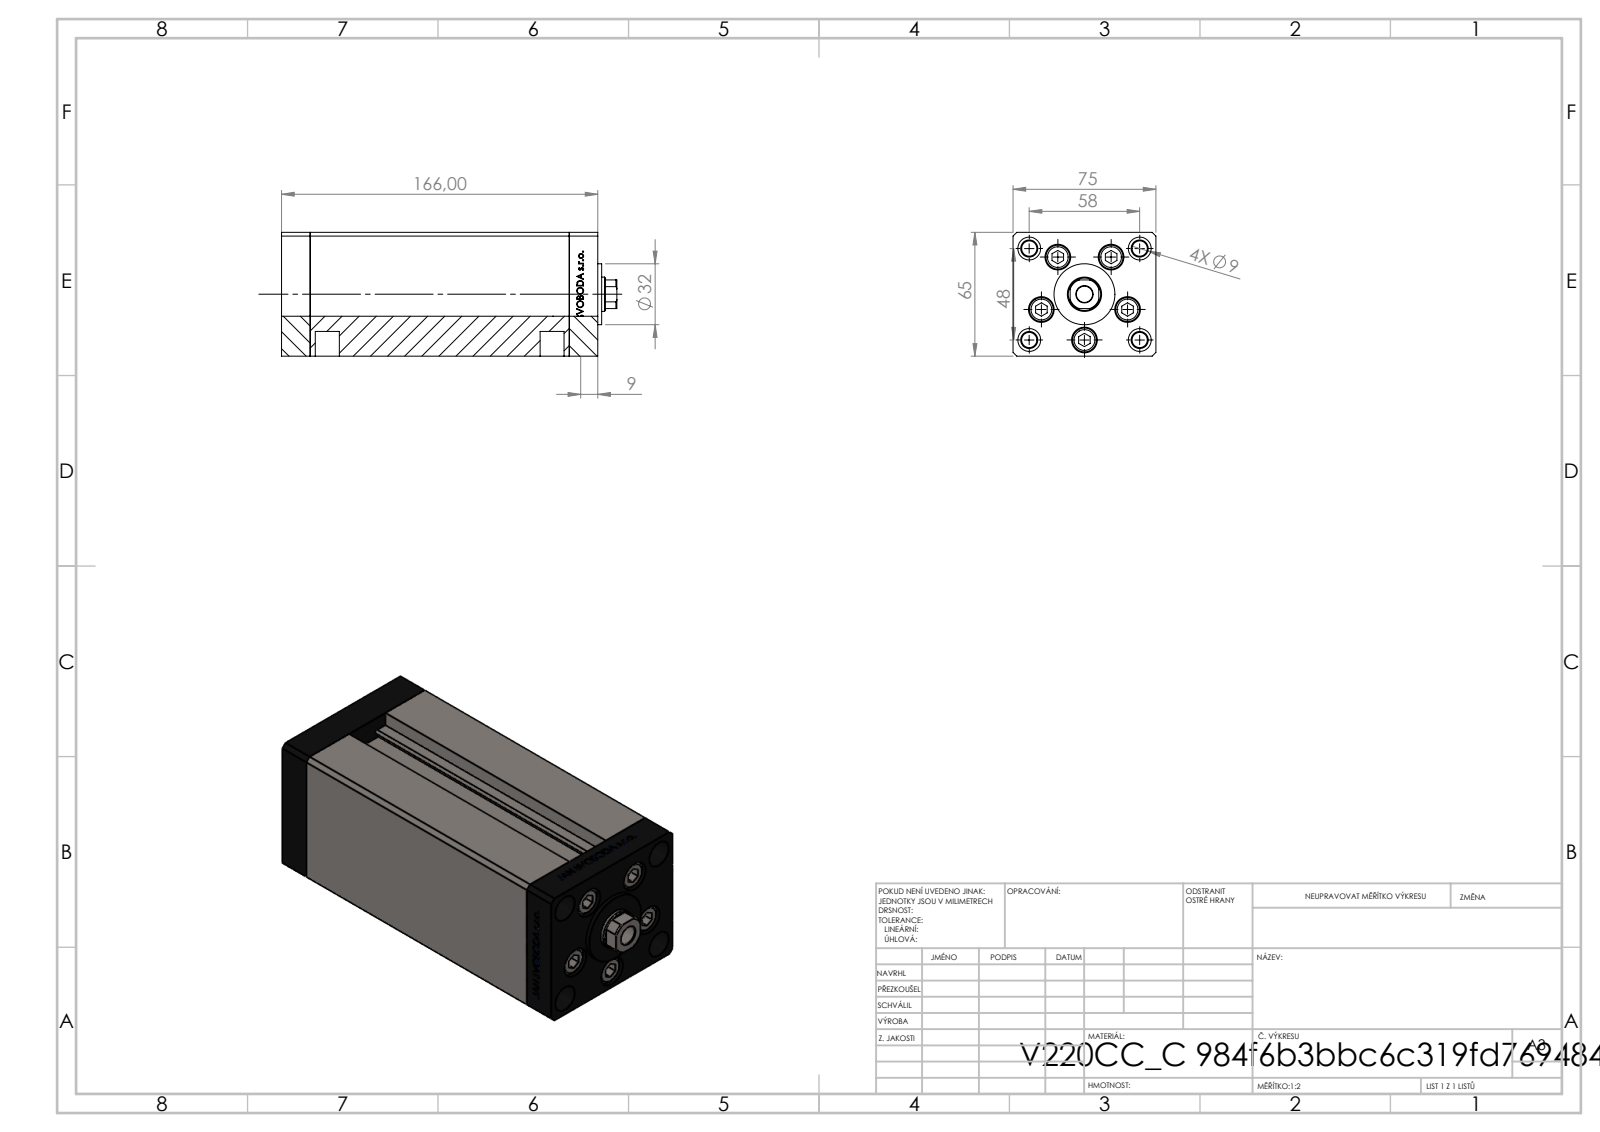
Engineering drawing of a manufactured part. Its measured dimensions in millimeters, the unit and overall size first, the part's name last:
Units: millimetres
Overall size (bounding box): 176 × 75 × 65
Round holes (diameter × count): ⌀9 ×9, ⌀13.5 ×5, ⌀2 ×4, ⌀8 ×4, ⌀12 ×4, ⌀13.16 ×4, ⌀8.5 ×1, ⌀12.5 ×1, ⌀18 ×1
Round bosses / shafts (diameter × count): ⌀8 ×5, ⌀12.5 ×4, ⌀32 ×1
Partial cylindrical surfaces — rounded edges, fillets, slot ends (radius × count): R0.93 ×2, R8.5 ×1
Main face-to-face distances: 75, 65, 15, 136, 151, 166, 28, 13, 142, 9
Hole centre spacings: 24, 37.64, 15.67, 17.22, 27.71, 28.83, 29, 32.63
Volume: 676 888 mm³ · Surface area: 143 721 mm²
Bodies: 13 solids, 1179 faces (542 planar, 175 cylindrical, 462 other)
Part name (STEP PRODUCT): V220C_VC_C; V220C FRONT; ALLEN BOLT; V220C_C MIDDLE (+1 more)
STEP written by: SolidWorks 2019 (CONFIG_CONTROL_DESIGN)
